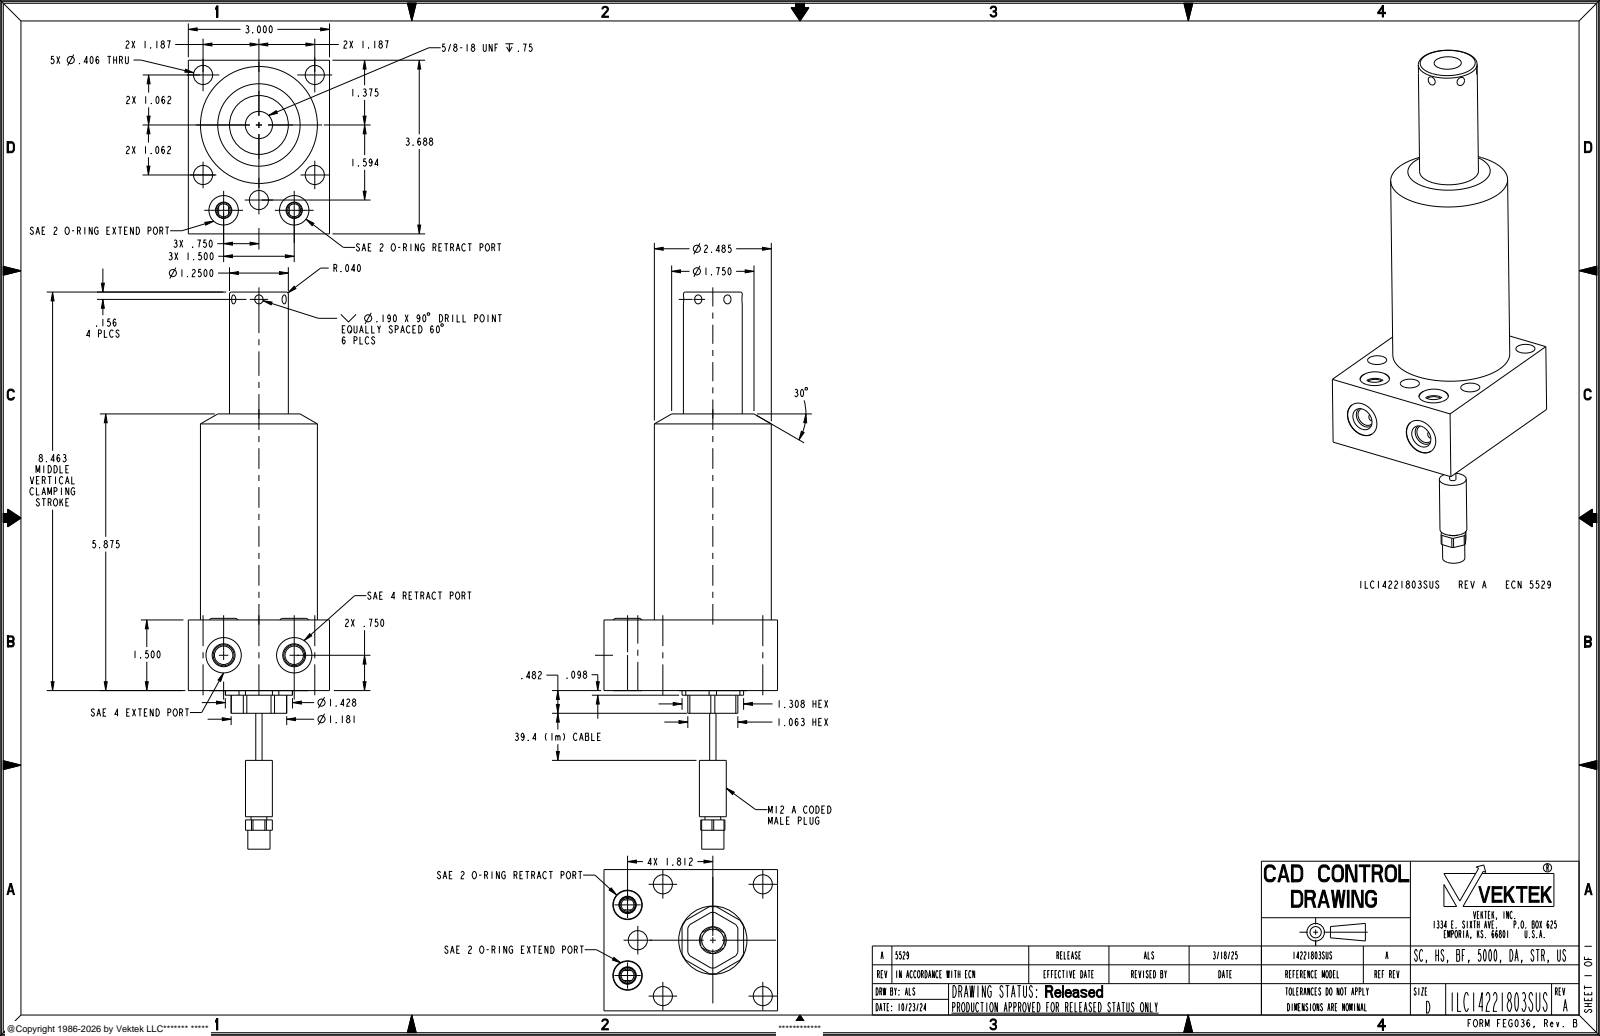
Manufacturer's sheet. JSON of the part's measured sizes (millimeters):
{"part_name": "ILC14221803SUS", "step_written_by": "CREO PARAMETRIC BY PTC INC, 2021164 (AUTOMOTIVE_DESIGN)", "units": "millimeters", "bodies": {"solids": 5, "faces": 173, "planar": 49, "cylindrical": 70, "other": 54}, "overall_size": [300.5, 93.7, 76.2], "volume_mm3": 656500, "surface_area_mm2": 70650, "round_holes": [[10.3, 5], [6.9, 2], [10, 2], [15.9, 2], [19.1, 2], [14.7, 1]], "round_bosses_or_shafts": [[63.1, 1], [36.8, 1], [31.8, 1], [15.9, 1], [14.5, 1], [12, 1], [8.5, 1], [3.4, 1]], "partial_cylinders_radius": [[15, 1], [18.1, 1]], "face_to_face_distances": [76.2, 38.1, 93.7, 149.2, 111.1, 12.2, 50.3, 161.5, 2.7, 35.4], "hole_center_spacings": [40.5, 19.8, 22, 33, 38.1, 49.8, 52.8, 53.9]}
